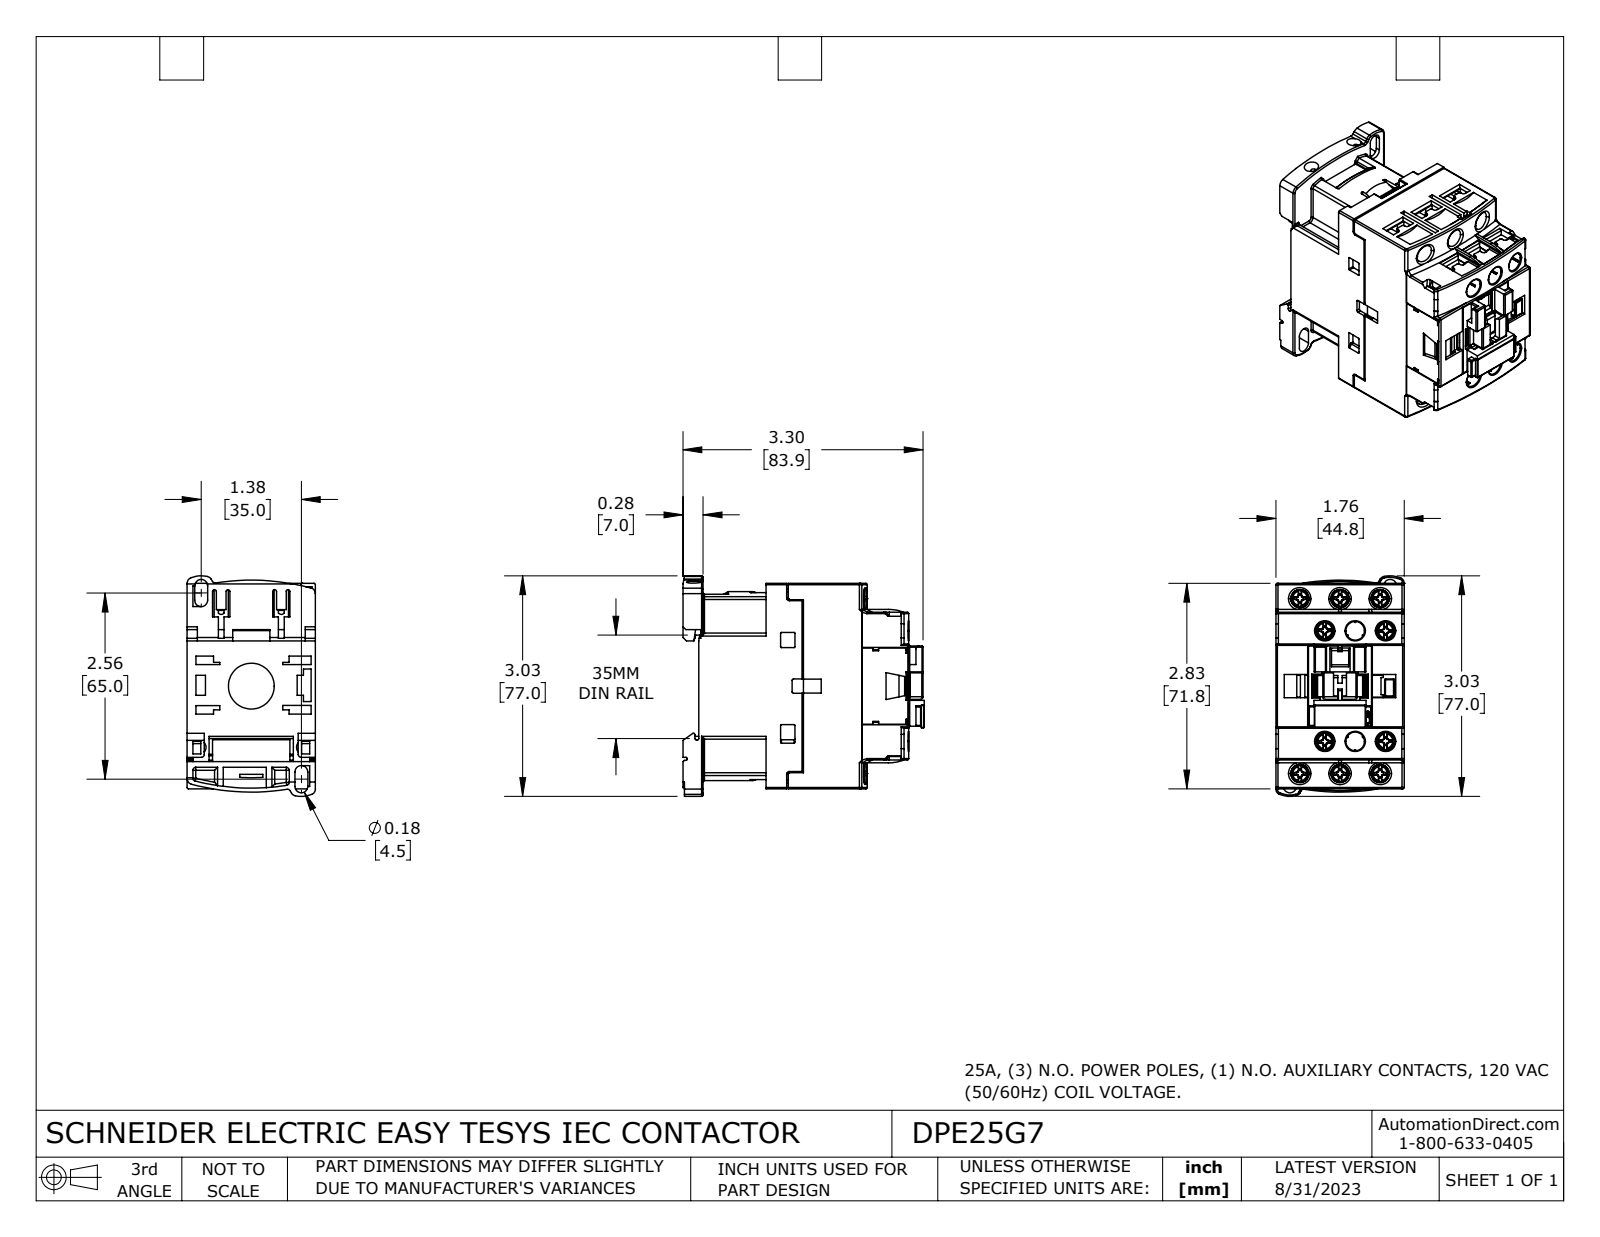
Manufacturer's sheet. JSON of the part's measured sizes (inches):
{"part_name": "DPE25G7", "step_written_by": "SolidWorks 2021 (CONFIG_CONTROL_DESIGN)", "units": "inches", "bodies": {"solids": 20, "faces": 3363, "planar": 2297, "cylindrical": 694, "other": 372}, "overall_size": [3.317, 3.031, 1.783], "volume_in3": 8.907, "surface_area_in2": 103.4, "round_holes": [[0.252, 6], [0.256, 6], [0.197, 2], [0.167, 1], [0.63, 1]], "round_bosses_or_shafts": [[0.138, 10], [0.108, 10], [0.315, 6]], "partial_cylinders_radius": [[0.02, 78], [0.012, 64], [0.039, 61], [0.006, 42], [0.016, 24], [0.63, 9], [0.024, 8], [0.079, 7]], "face_to_face_distances": [0.047, 1.764, 1.717, 0.321, 1.128, 0.807, 0.35, 2.78, 1.366, 1.118], "hole_center_spacings": [0.417, 0.488, 0.551, 0.558, 0.788, 0.878, 1.321, 1.576]}
